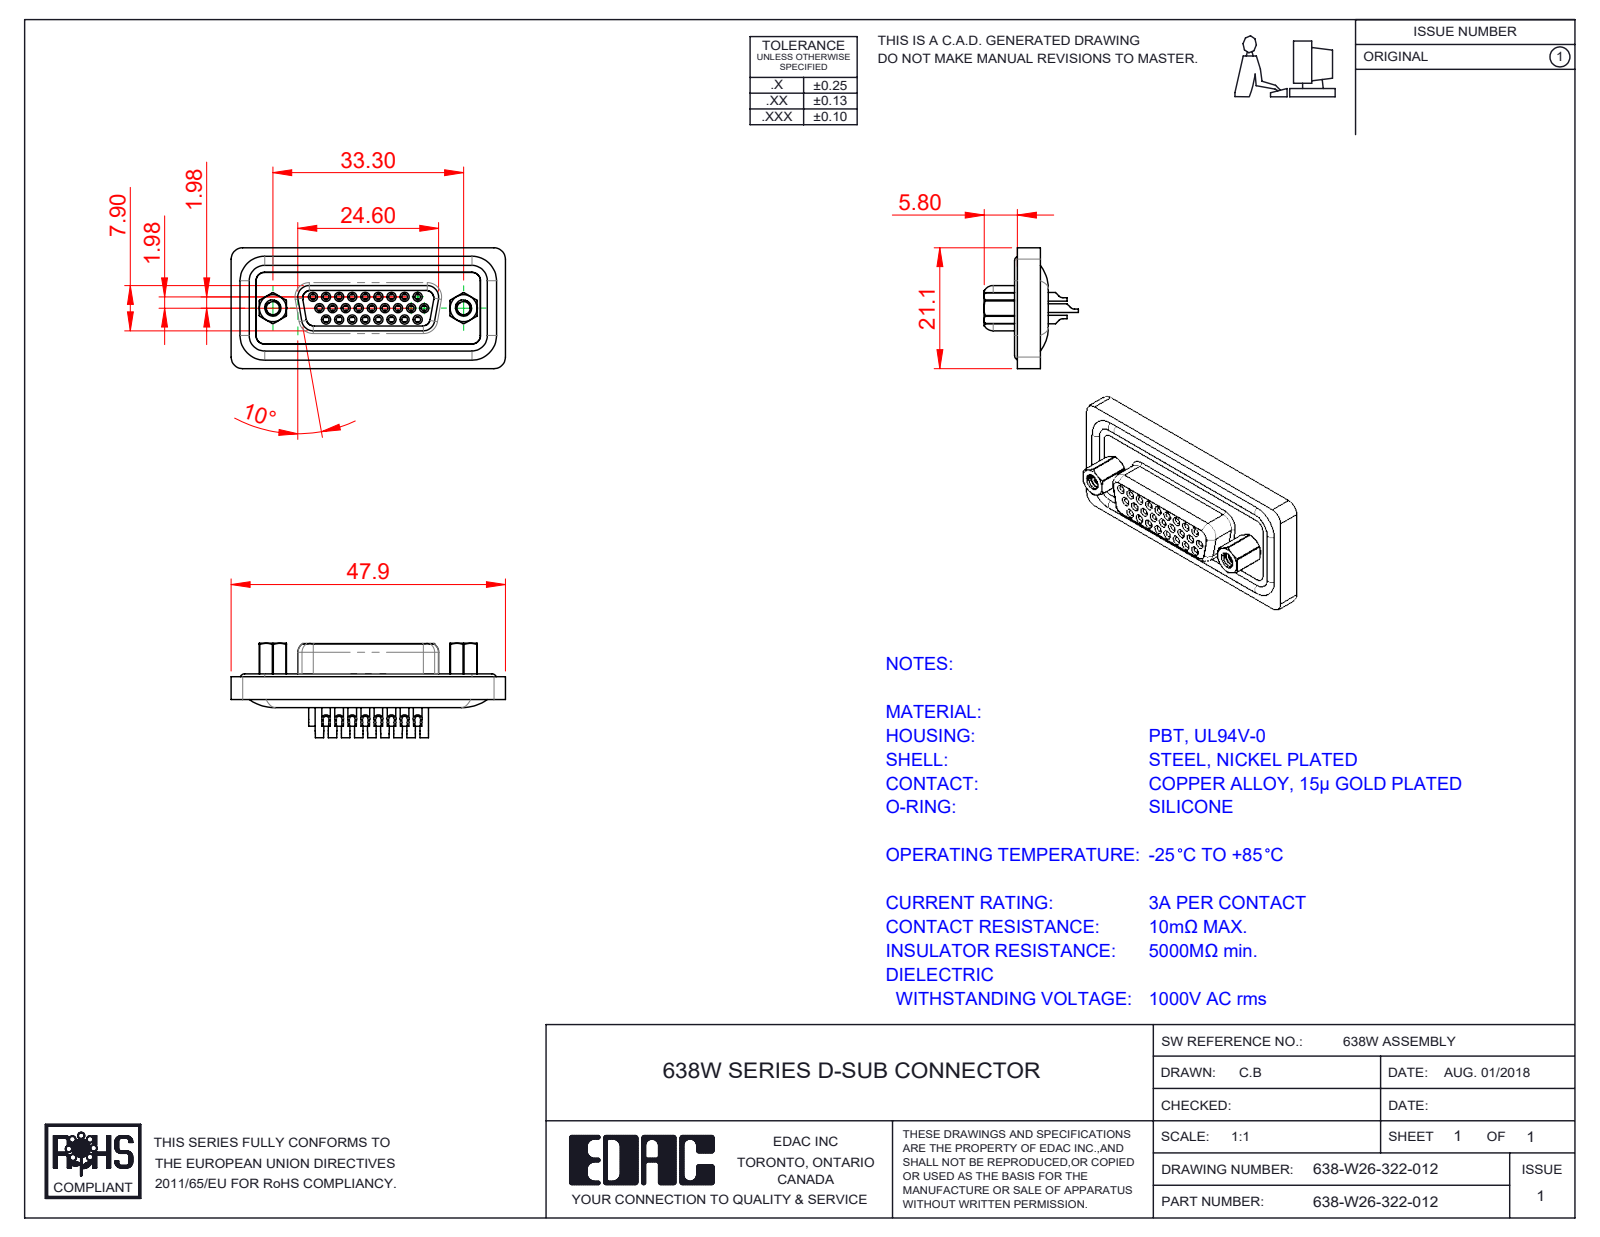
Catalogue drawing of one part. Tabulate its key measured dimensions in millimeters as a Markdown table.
| quantity | value |
| --- | --- |
| part name | 638-W26-322-012; 638W 4-40 Hex Standoff; 638W 4-40 Threaded Rivet; 638W Contact Row 3_22 (+5 more) |
| STEP written by | SolidWorks 2016 (CONFIG_CONTROL_DESIGN) |
| units | millimeters |
| bodies | 34 solids, 1903 faces (543 planar, 814 cylindrical, 546 other) |
| overall size | 47.89 × 21.1 × 16.5 |
| volume | 5 433 mm³ |
| surface area | 11 156 mm² |
| round holes (diameter × count) | 1 × 26, 1.1 × 26, 1.5 × 26, 1.7 × 26, 1.8 × 26, 2 × 26, 2.26 × 2, 2.29 × 2, 4 × 2, 4.8 × 2, 5 × 2 |
| round bosses / shafts (diameter × count) | 1.6 × 30, 2.2 × 26, 1.5 × 26, 4.9 × 2, 2.79 × 2, 5 × 1 |
| partial cylindrical surfaces (radius × count) | 2 × 16, 1.5 × 14, 1.35 × 8, 2.7 × 6, 0.5 × 4, 0.9 × 4, 1.6 × 4, 1.75 × 4 |
| main face-to-face distances | 0.4, 1.8, 2.9, 2.5, 1.1, 1.6, 0.5, 7.45, 13.65, 0.7 |
| hole center spacings | 3.96, 2.28, 4.57, 6.05, 2.29, 8.24, 6.86, 6.04 |
